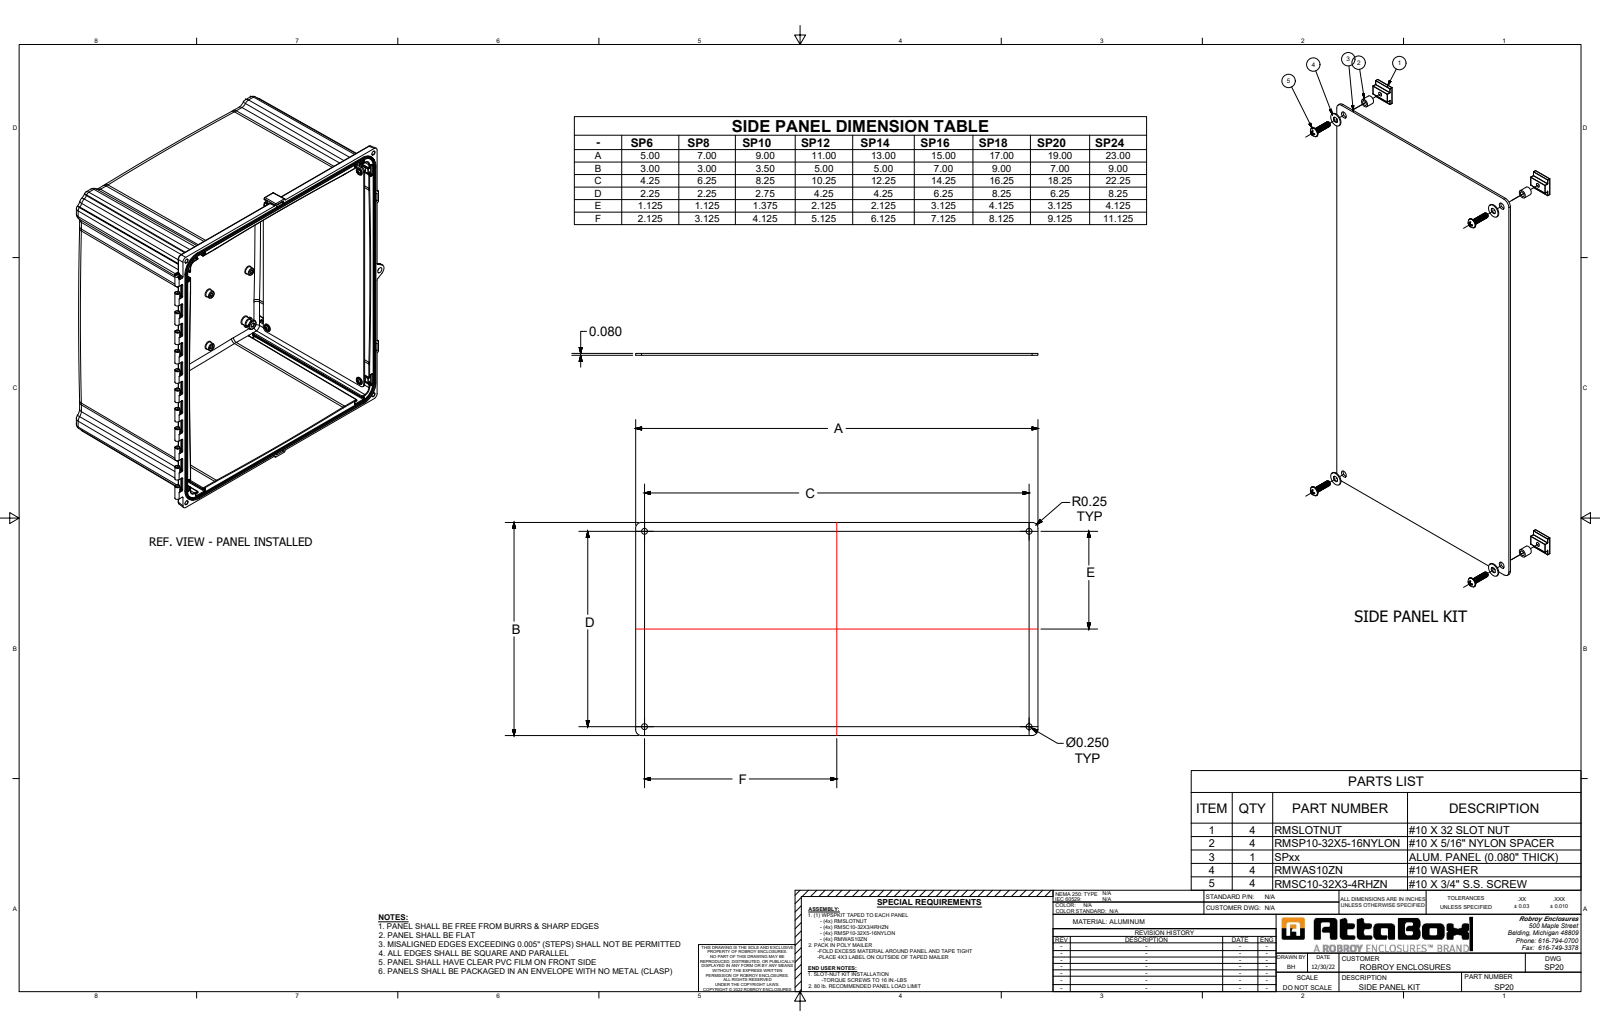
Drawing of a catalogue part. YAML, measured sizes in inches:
part_name: "SP20_Default"
step_written_by: "SolidWorks 2023 (CONFIG_CONTROL_DESIGN)"
units: inches
bodies: {solids: 1, faces: 14, planar: 6, cylindrical: 8, other: 0}
overall_size: [19, 7, 0.08]
volume: 10.62
surface_area: 269.9
round_holes:
  - {diameter: 0.25, count: 4}
partial_cylinders:
  - {radius: 0.25, count: 4}
face_to_face_distances: [0.08, 7, 19]
hole_center_spacings: [6.25, 18.25, 19.29]
